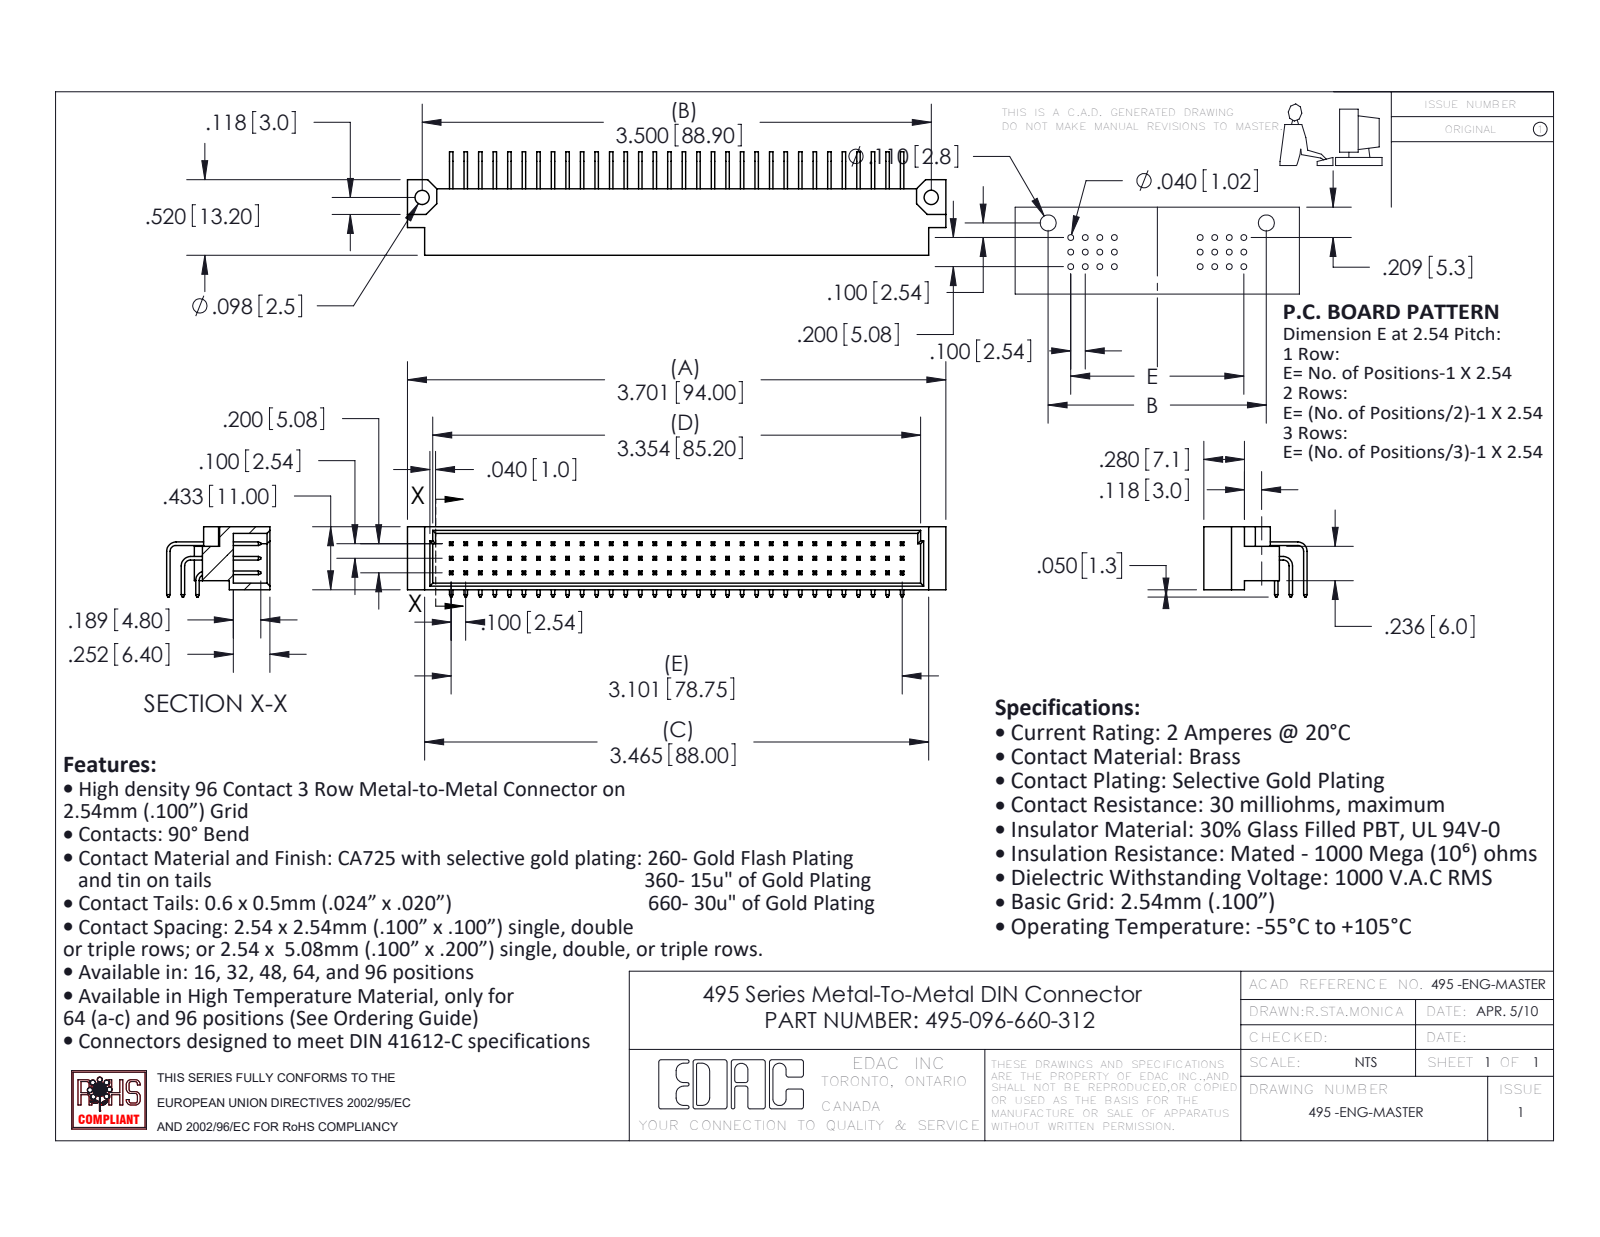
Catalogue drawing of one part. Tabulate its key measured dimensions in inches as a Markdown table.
| quantity | value |
| --- | --- |
| part name | 495-290-2; 495-290-3; 495-290-1; 495 Part_96 (+1 more) |
| STEP written by | SolidWorks 2020 (AUTOMOTIVE_DESIGN) |
| units | inches |
| bodies | 97 solids, 2161 faces (1965 planar, 196 cylindrical, 0 other) |
| overall size | 3.701 × 0.711 × 0.483 |
| volume | 0.404 in³ |
| surface area | 17.74 in² |
| round holes (diameter × count) | 0.098 × 2 |
| partial cylindrical surfaces (radius × count) | 0.04 × 3, 0.065 × 3 |
| main face-to-face distances | 0.1, 0.024, 0.2, 0.205, 0.045, 0.388, 0.124, 0.076, 0.433, 0.343 |
| hole center spacings | 3.5 |
